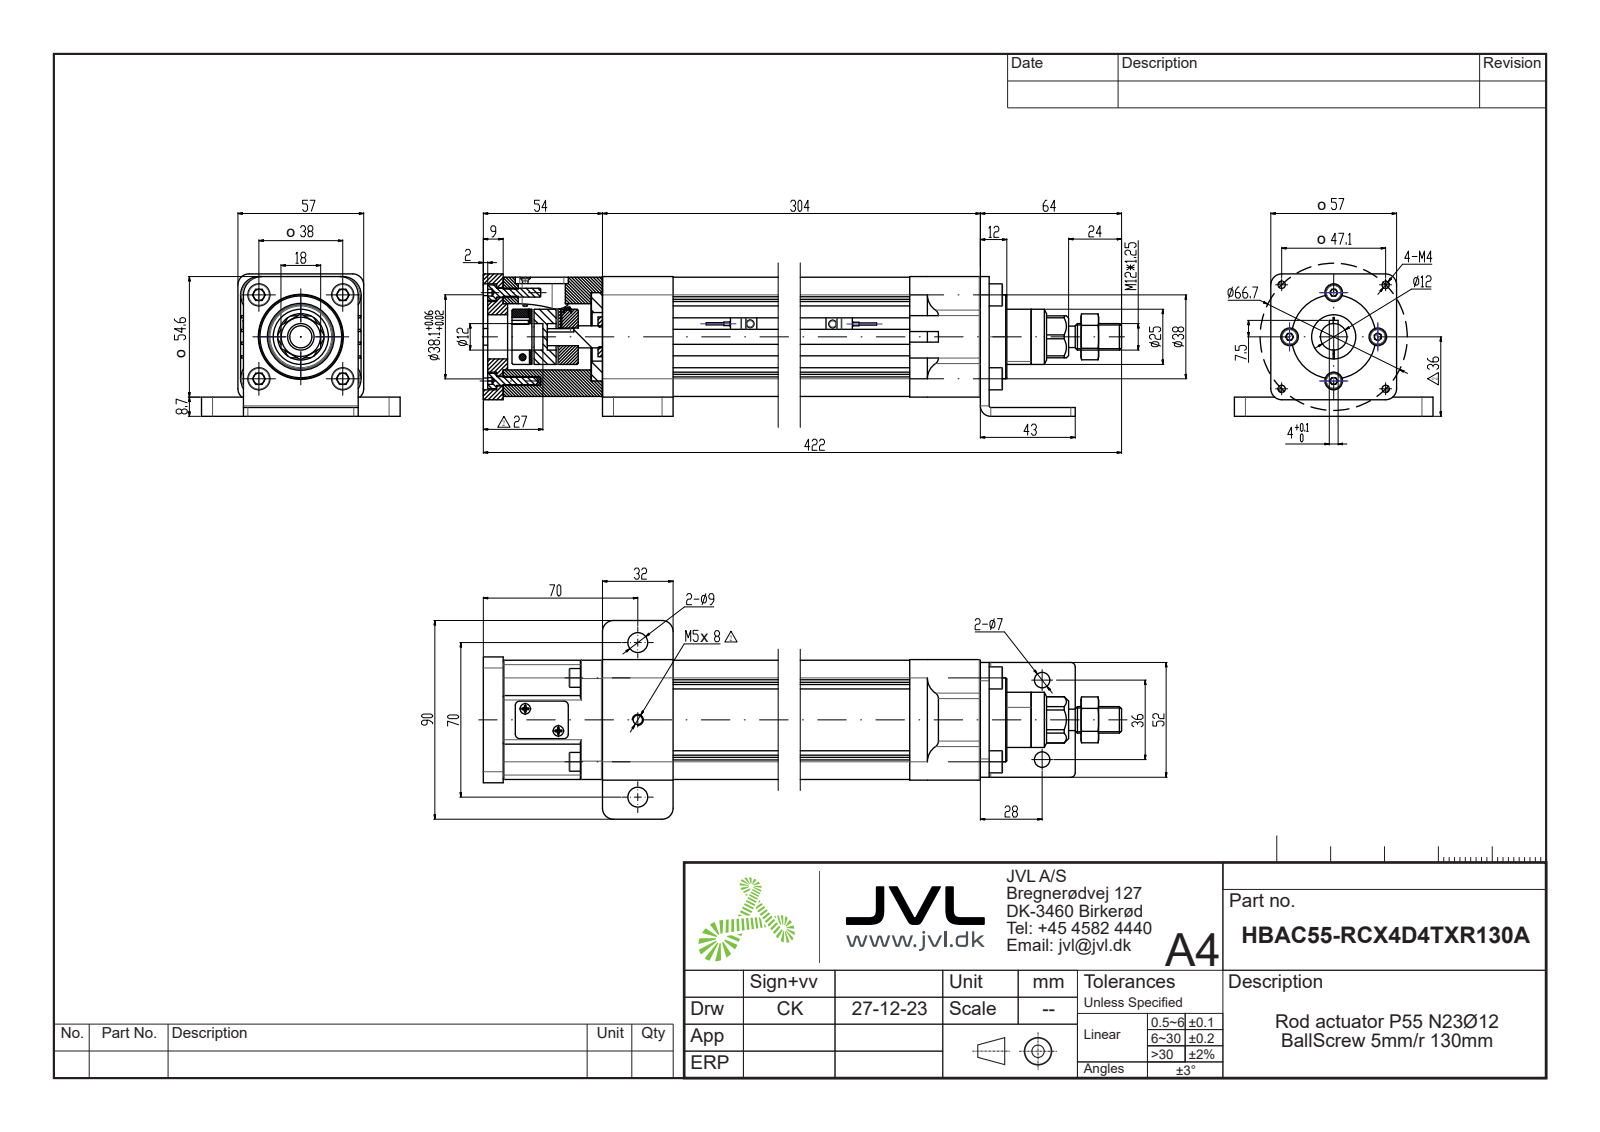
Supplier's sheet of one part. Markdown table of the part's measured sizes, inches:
| quantity | value |
| --- | --- |
| part name | ZL-40-100-4X4; HBAC55-RCX4D4TXR130A; 2519-100-4X4; 40__________-100-4X4 (+7 more) |
| STEP written by | SolidWorks 2023 (AUTOMOTIVE_DESIGN) |
| units | inches |
| bodies | 69 solids, 2621 faces (938 planar, 781 cylindrical, 902 other) |
| overall size | 16.693 × 3.543 × 2.539 |
| volume | 48.53 in³ |
| surface area | 526.5 in² |
| round holes (diameter × count) | 0.13 × 14, 0.169 × 6, 0.315 × 5, 0.177 × 4, 0.197 × 4, 0.252 × 4, 0.256 × 4, 0.26 × 4, 0.374 × 4, 0.081 × 2, 0.098 × 2, 0.114 × 2 |
| round bosses / shafts (diameter × count) | 0.276 × 10, 0.157 × 10, 0.335 × 6, 0.394 × 4, 0.354 × 4, 0.236 × 4, 0.118 × 4, 0.217 × 2 |
| partial cylindrical surfaces (radius × count) | 0.008 × 40, 0.02 × 20, 0.079 × 18, 0.295 × 13, 0.039 × 12, 0.197 × 10, 0.327 × 10, 0.118 × 8 |
| main face-to-face distances | 2.126, 0.197, 2.138, 0.354, 0.157, 2.48, 1.26, 1.772, 0.177, 1.949 |
| hole center spacings | 0.561, 0.749, 0.939, 1.231, 1.311, 1.456, 1.685, 1.708 |
